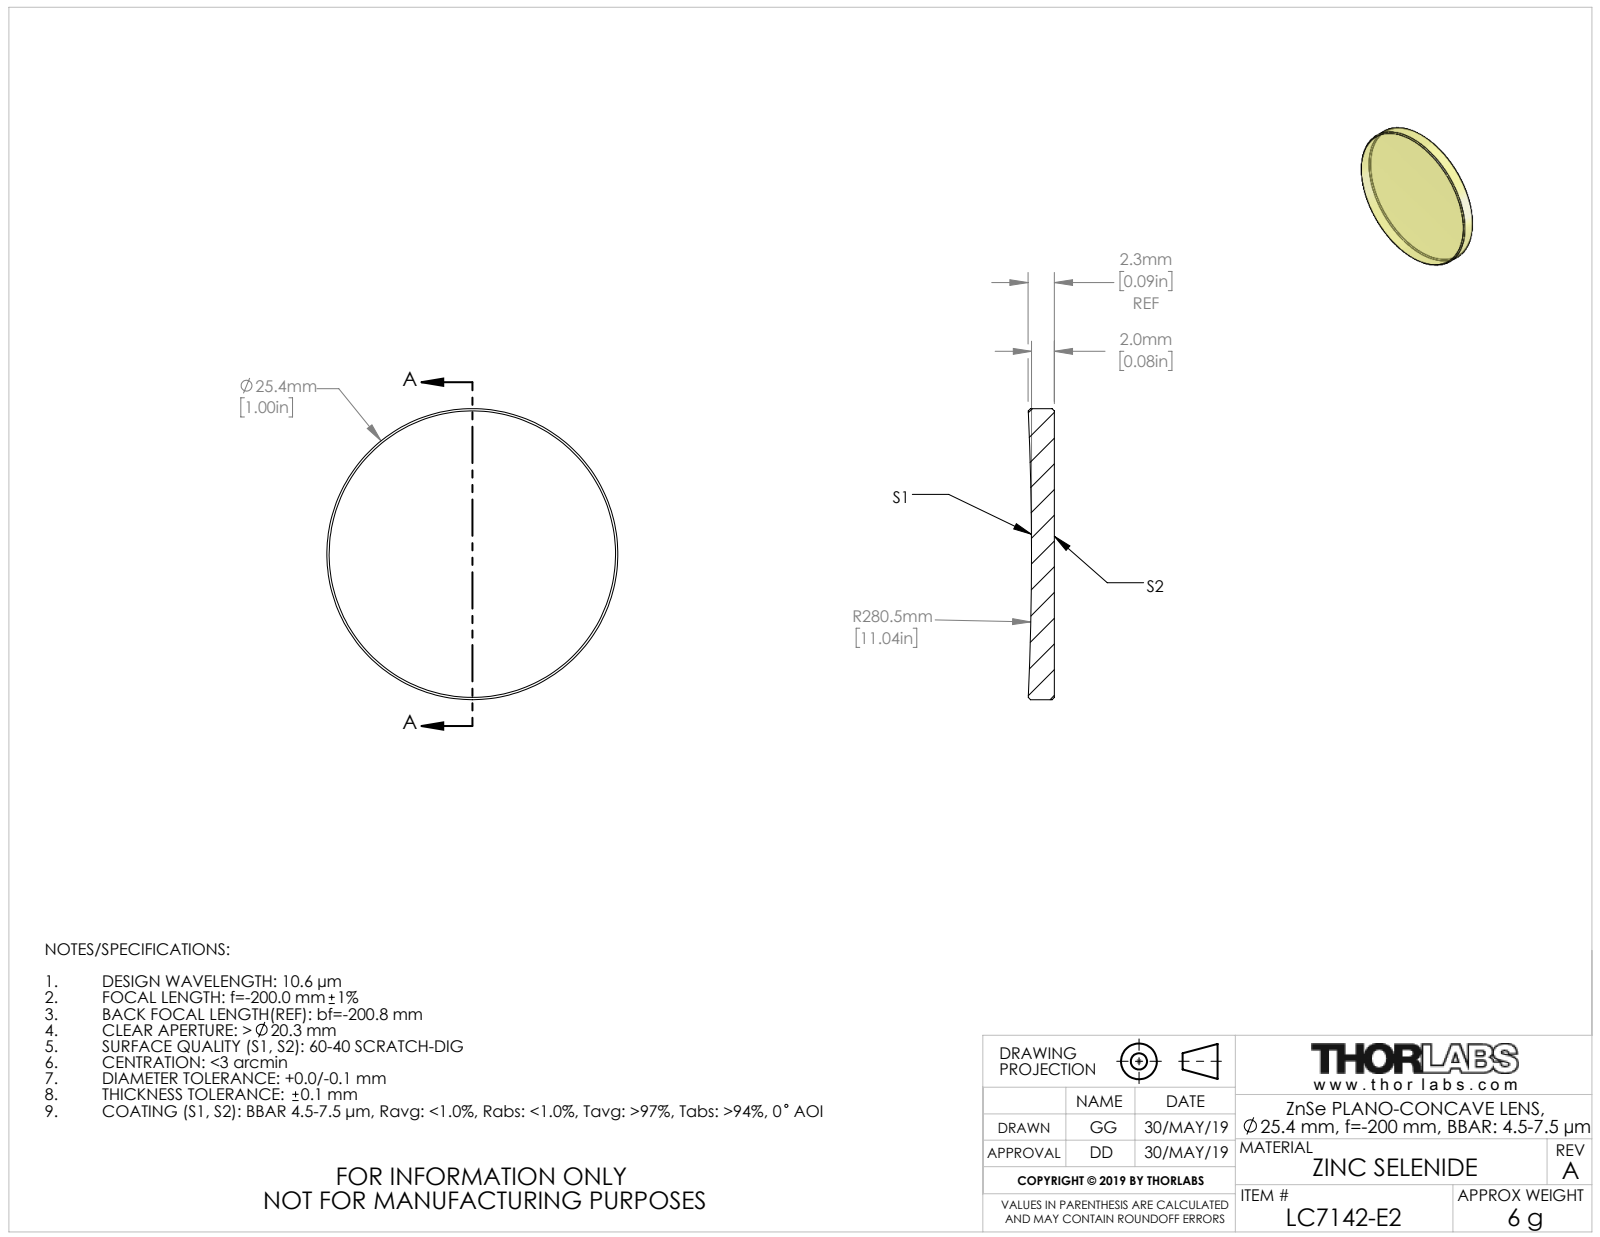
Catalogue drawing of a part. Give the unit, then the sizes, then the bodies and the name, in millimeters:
Units: millimetres
Overall size (bounding box): 25.4 × 25.4 × 2.28
Round bosses / shafts (diameter × count): ⌀25.4 ×1
Volume: 1 083 mm³ · Surface area: 1 177 mm²
Bodies: 1 solid, 9 faces (1 planar, 2 cylindrical, 6 other)
Part name (STEP PRODUCT): TTN047624-E0W
STEP written by: SolidWorks 2018 (CONFIG_CONTROL_DESIGN)
